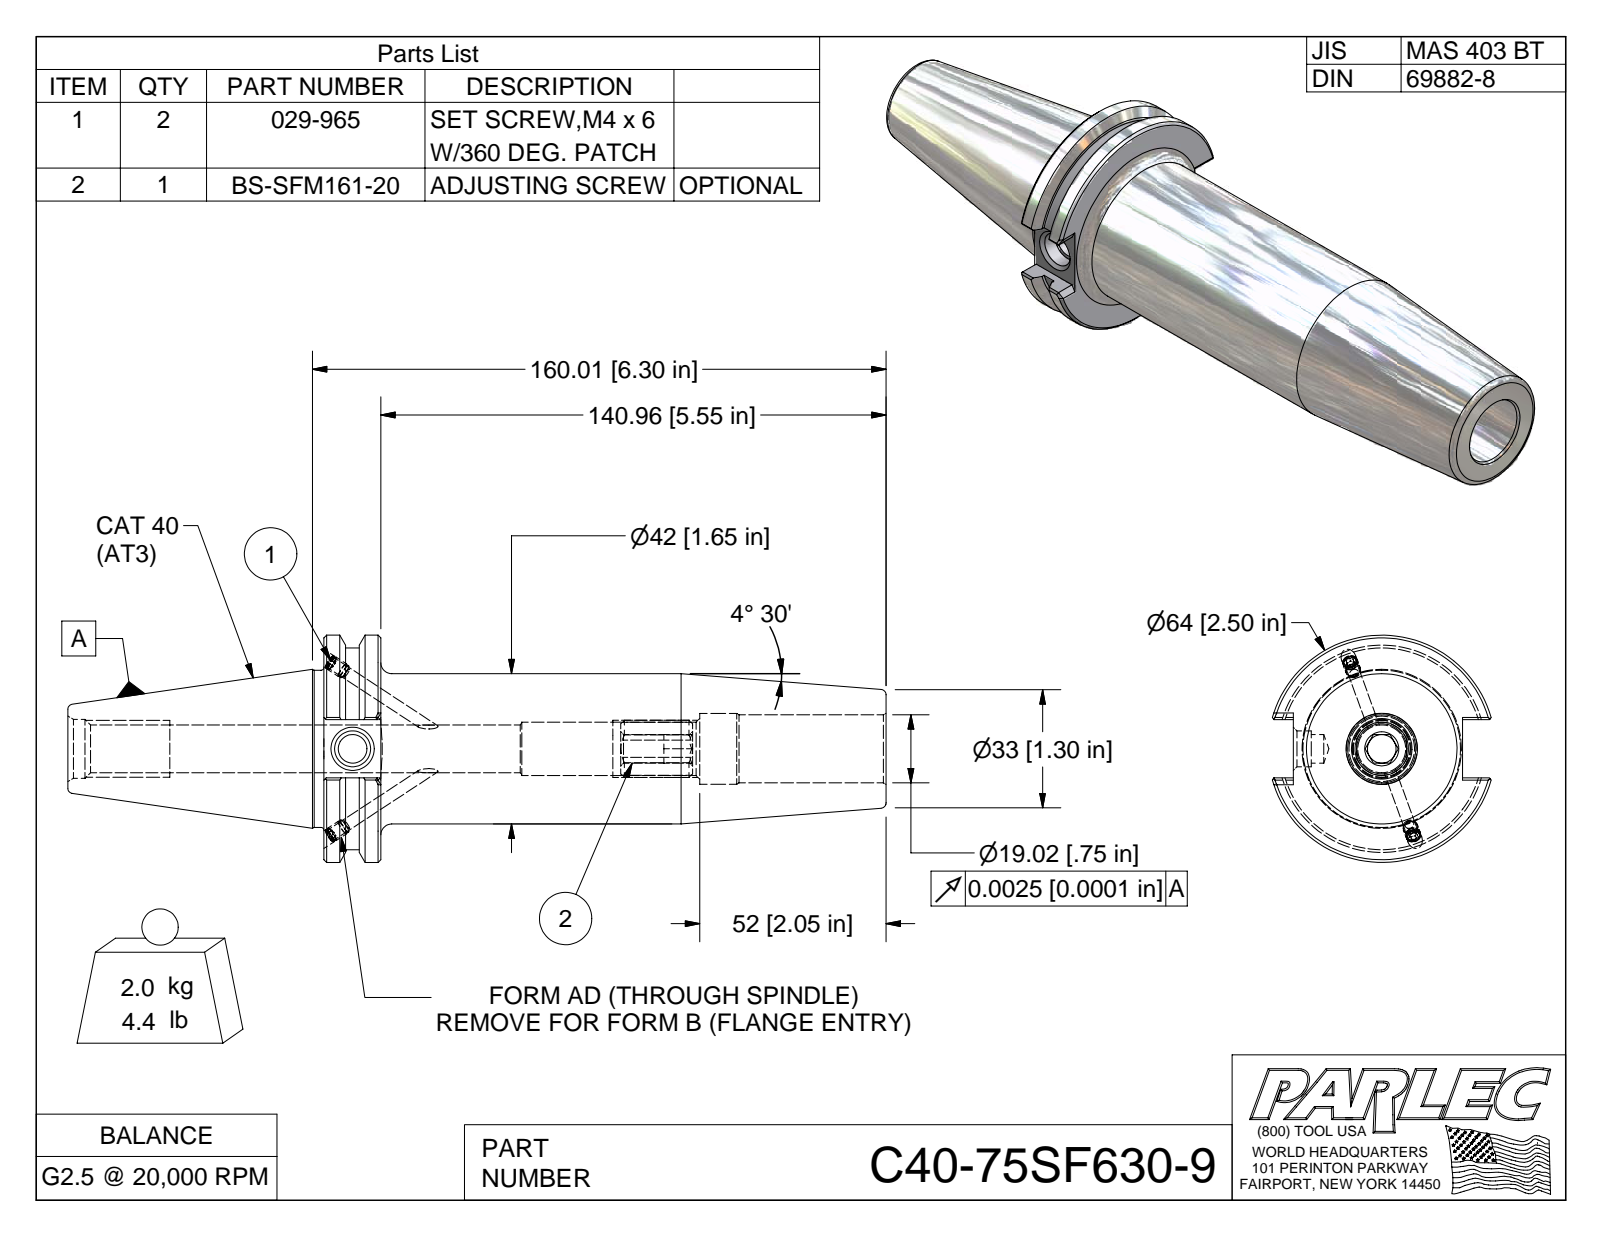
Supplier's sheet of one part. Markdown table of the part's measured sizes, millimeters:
| quantity | value |
| --- | --- |
| part name | C40-75SF630-9; C40BC-75SF630-9-1; 029-965; BS-SFM161-20 |
| STEP written by | Autodesk Inventor 2009 (AUTOMOTIVE_DESIGN) |
| units | millimeters |
| bodies | 4 solids, 130 faces (65 planar, 22 cylindrical, 43 other) |
| overall size | 228.3 × 63.5 × 61 |
| volume | 253 000 mm³ |
| surface area | 46 970 mm² |
| round holes (diameter × count) | 3.3 × 2, 4.1 × 2, 19 × 1, 19.8 × 1 |
| round bosses / shafts (diameter × count) | 4.2 × 2, 4 × 2, 63.5 × 1, 56.4 × 1, 43.9 × 1, 42 × 1 |
| partial cylindrical surfaces (radius × count) | 8 × 1 |
| main face-to-face distances | 15.9, 156.8, 141, 16.3, 29.6, 15.6, 14, 47.2, 31.7, 17.7 |
